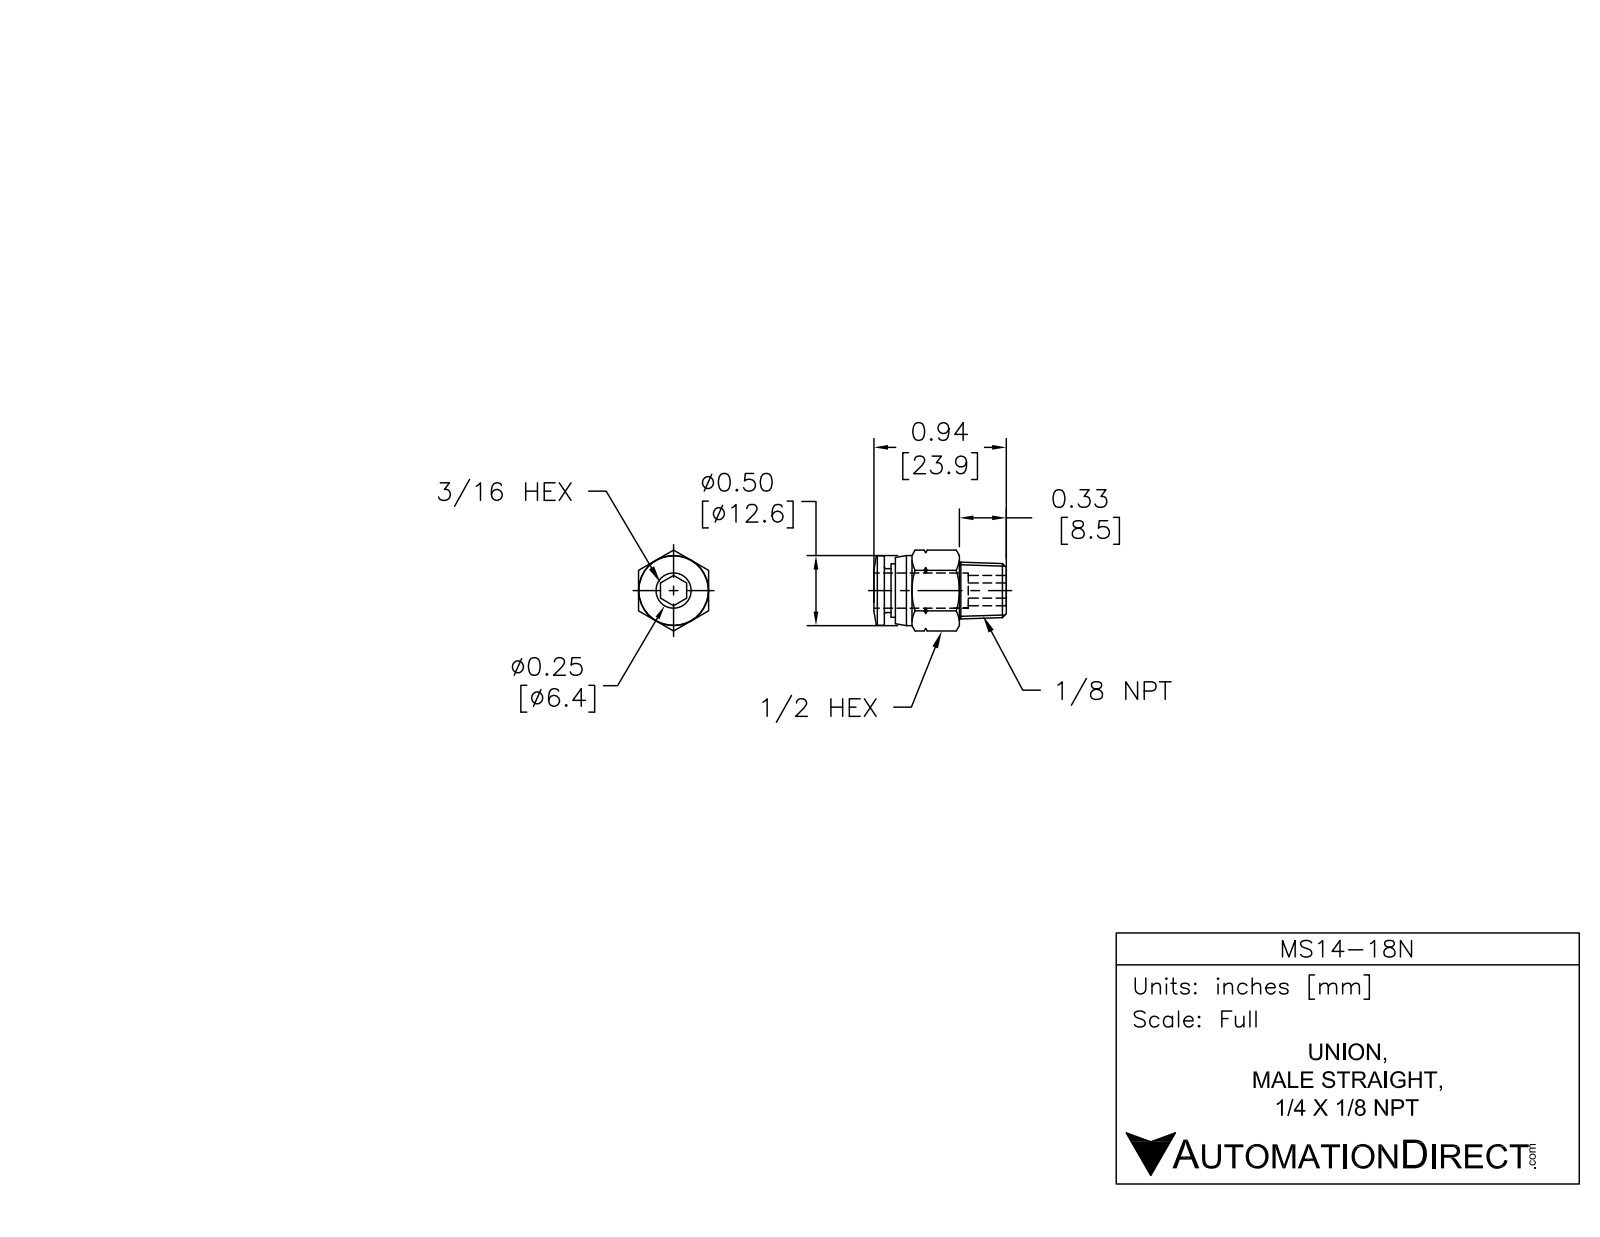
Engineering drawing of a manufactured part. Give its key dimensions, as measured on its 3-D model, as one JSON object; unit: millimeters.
{"part_name": "PC1-4--N01", "step_written_by": "Autodesk Inventor 2008 (AUTOMOTIVE_DESIGN)", "units": "millimeters", "bodies": {"solids": 1, "faces": 50, "planar": 12, "cylindrical": 6, "other": 32}, "overall_size": [24, 14.66, 12.7], "volume_mm3": 1864, "surface_area_mm2": 1671, "round_holes": [[4.8, 1], [6.55, 1]], "round_bosses_or_shafts": [[12.7, 1], [12.6, 1], [9.7, 1], [7.95, 1]], "face_to_face_distances": [12.7, 13.6, 11.6, 2, 8.5, 20.1, 22.1, 20.9, 12.4, 0.8]}
